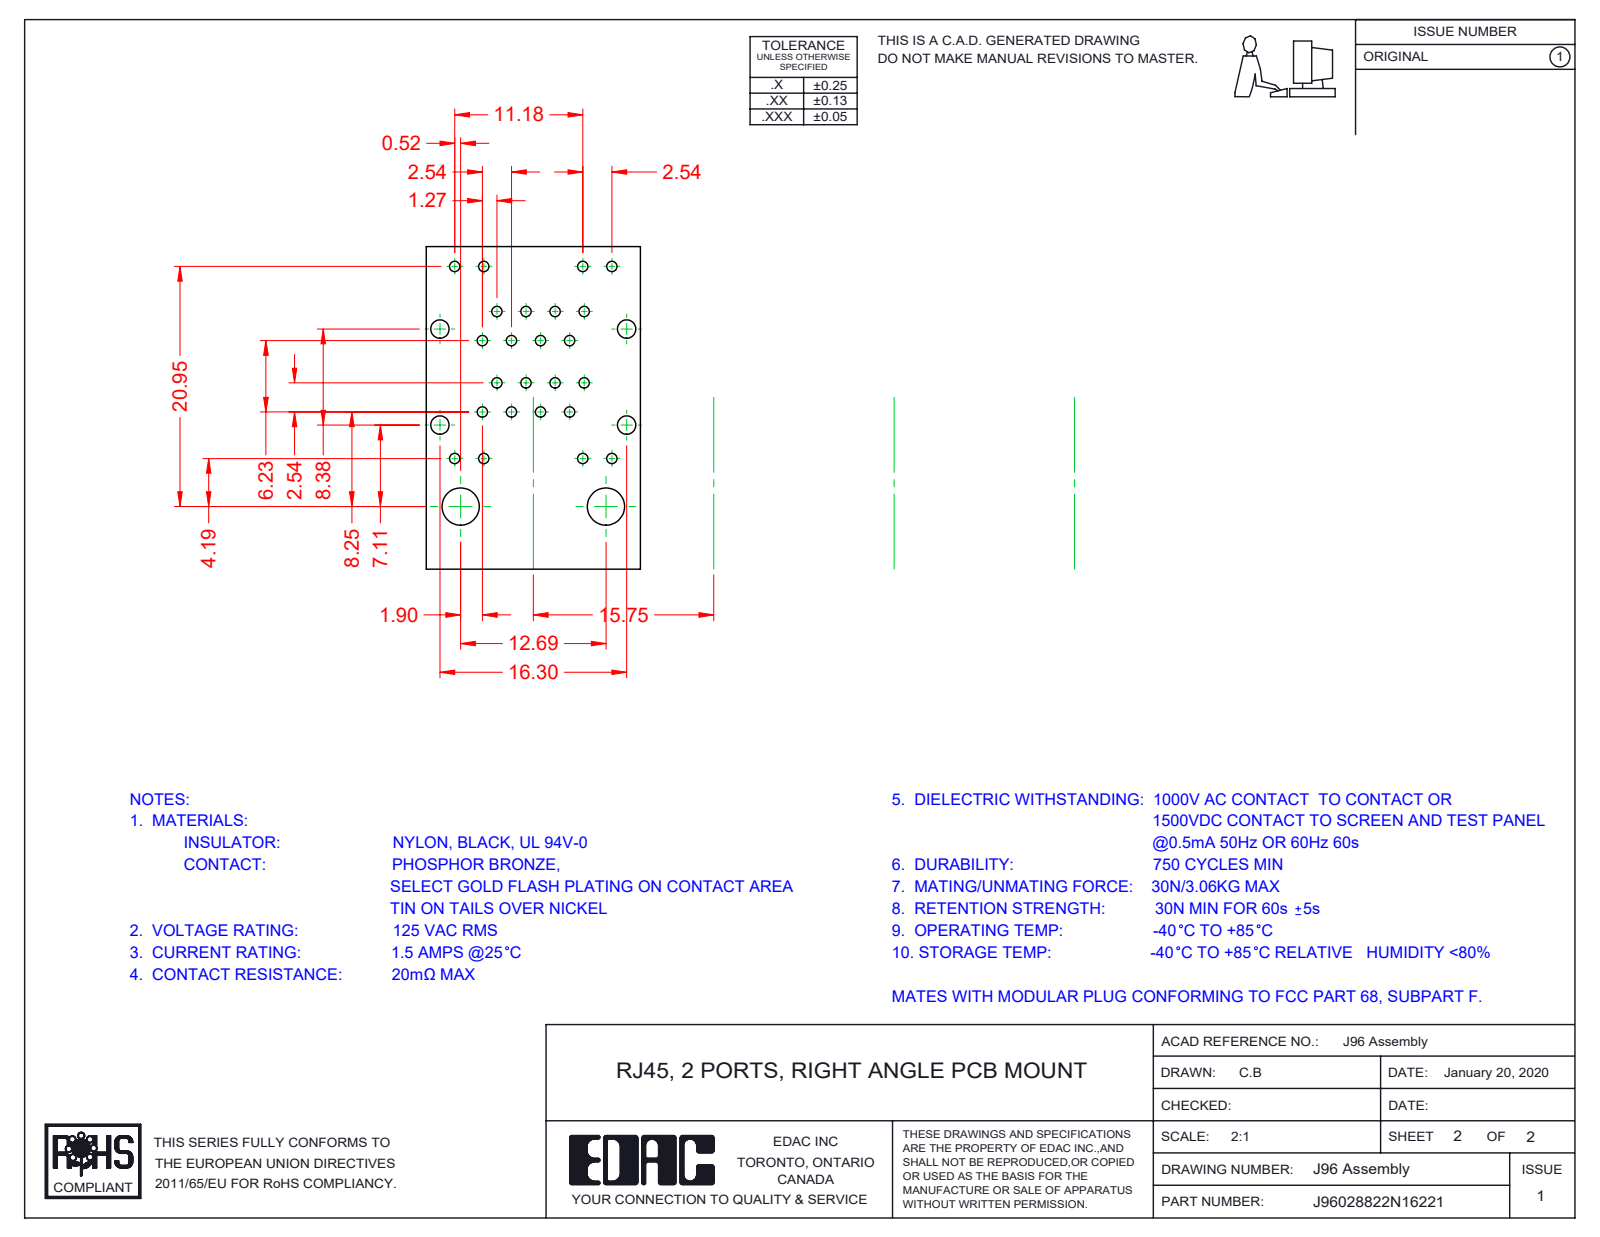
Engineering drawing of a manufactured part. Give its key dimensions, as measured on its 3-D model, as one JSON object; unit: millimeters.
{"part_name": "96 Contact Lock Upper; J96028822N16221; 96 Contacts Upper; 96 Shield_2 Ports LED - EMI (+8 more)", "step_written_by": "SolidWorks 2016 (CONFIG_CONTROL_DESIGN)", "units": "millimeters", "bodies": {"solids": 27, "faces": 2421, "planar": 1865, "cylindrical": 450, "other": 106}, "overall_size": [31.38, 28.68, 16.8], "volume_mm3": 6849, "surface_area_mm2": 19094, "partial_cylinders_radius": [[0.25, 48], [0.15, 32], [0.35, 24], [0.5, 16], [1, 16], [0.2, 14], [0.7, 9], [2, 5]], "face_to_face_distances": [16.3, 16.1, 1.75, 16.5, 14.75, 1.55, 14.55, 0.53, 1.48, 11.2]}
